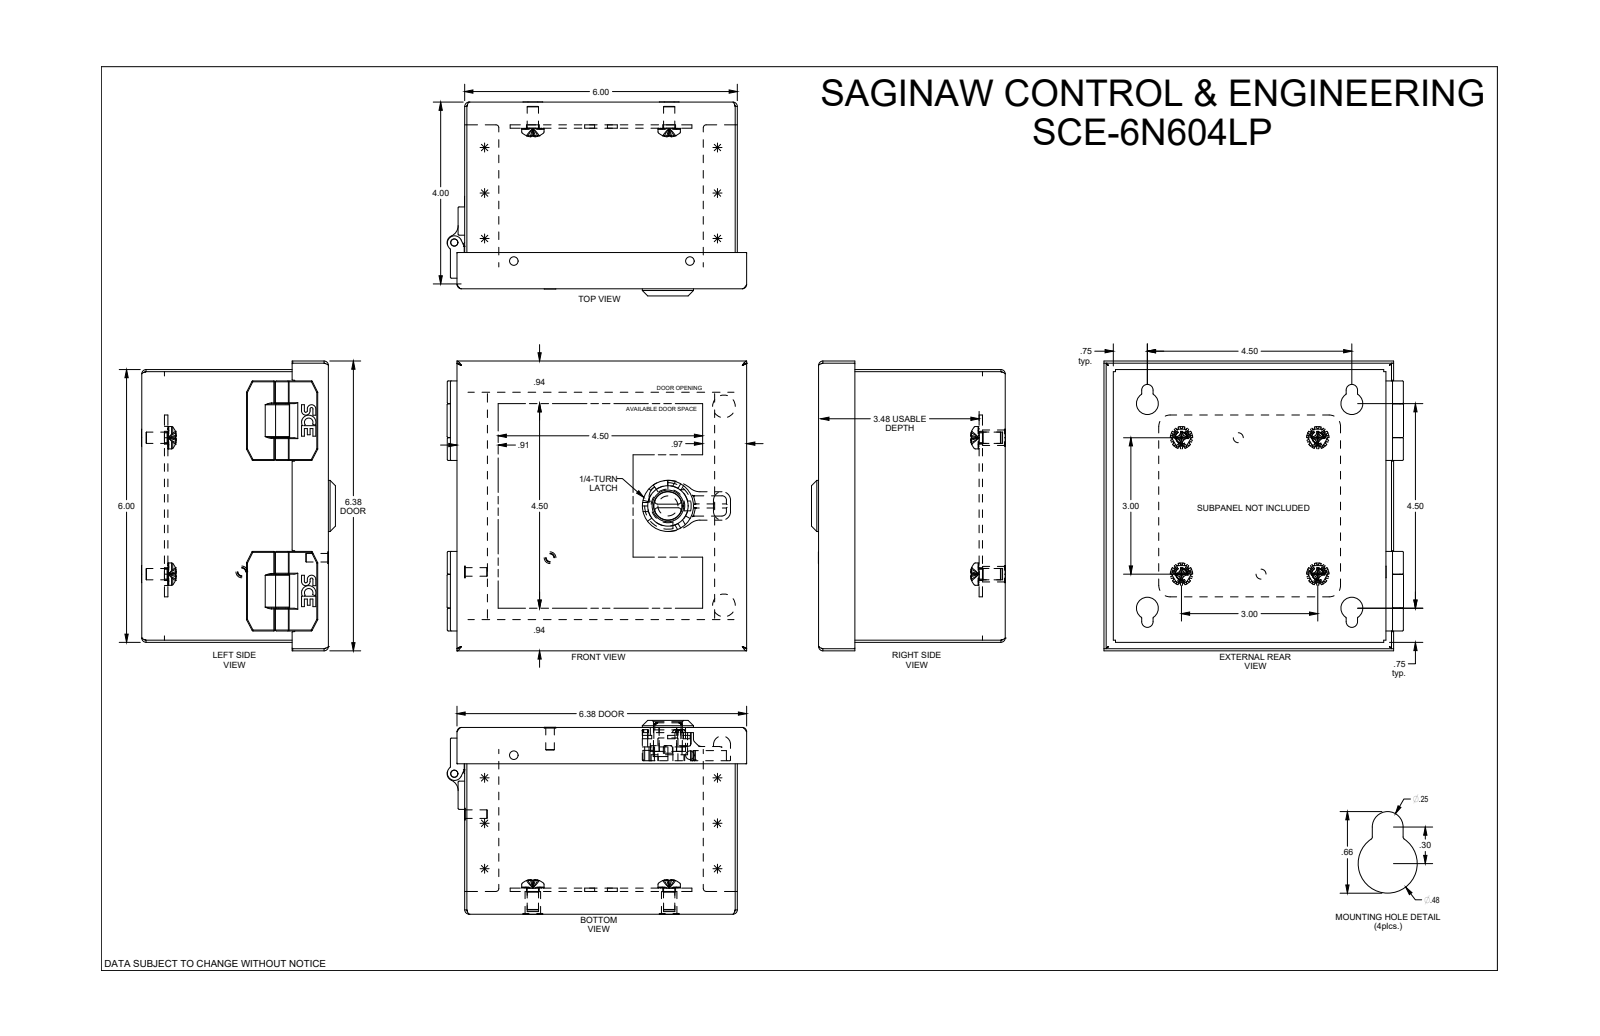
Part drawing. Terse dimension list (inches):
name: SCE-6N604LP_REV3
written by: SolidWorks 2021 (AUTOMOTIVE_DESIGN)
unit: in
bodies: 21 solids, 742 faces (267 planar, 308 cylindrical, 167 other)
size: 6.593 × 6.375 × 4.267
volume: 14.81 in³; area: 468.7 in²
holes: 4× ⌀0.25, 4× ⌀0.281, 4× ⌀0.343, 4× ⌀0.48, 2× ⌀0.218, 2× ⌀0.329, 1× ⌀0.158, 1× ⌀0.187, 1× ⌀0.193, 1× ⌀0.44, 1× ⌀0.635, 1× ⌀0.891
bosses: 4× ⌀0.341, 2× ⌀0.5, 2× ⌀0.337, 2× ⌀0.323, 2× ⌀0.248, 2× ⌀0.237, 2× ⌀0.16, 1× ⌀1.125
rounds: 95× R0.02, 25× R0.06, 16× R0.015, 13× R0.01, 6× R0.055, 6× R0.25, 4× R0.125, 3× R0.188
face distances: 0.06, 5.94, 4.047, 5.88, 6, 3.987, 4.107, 3.94, 0.107, 6.315
hole spacings: 3.824, 1.061, 3, 4.5, 5.303, 1.25, 1.5, 1.75
